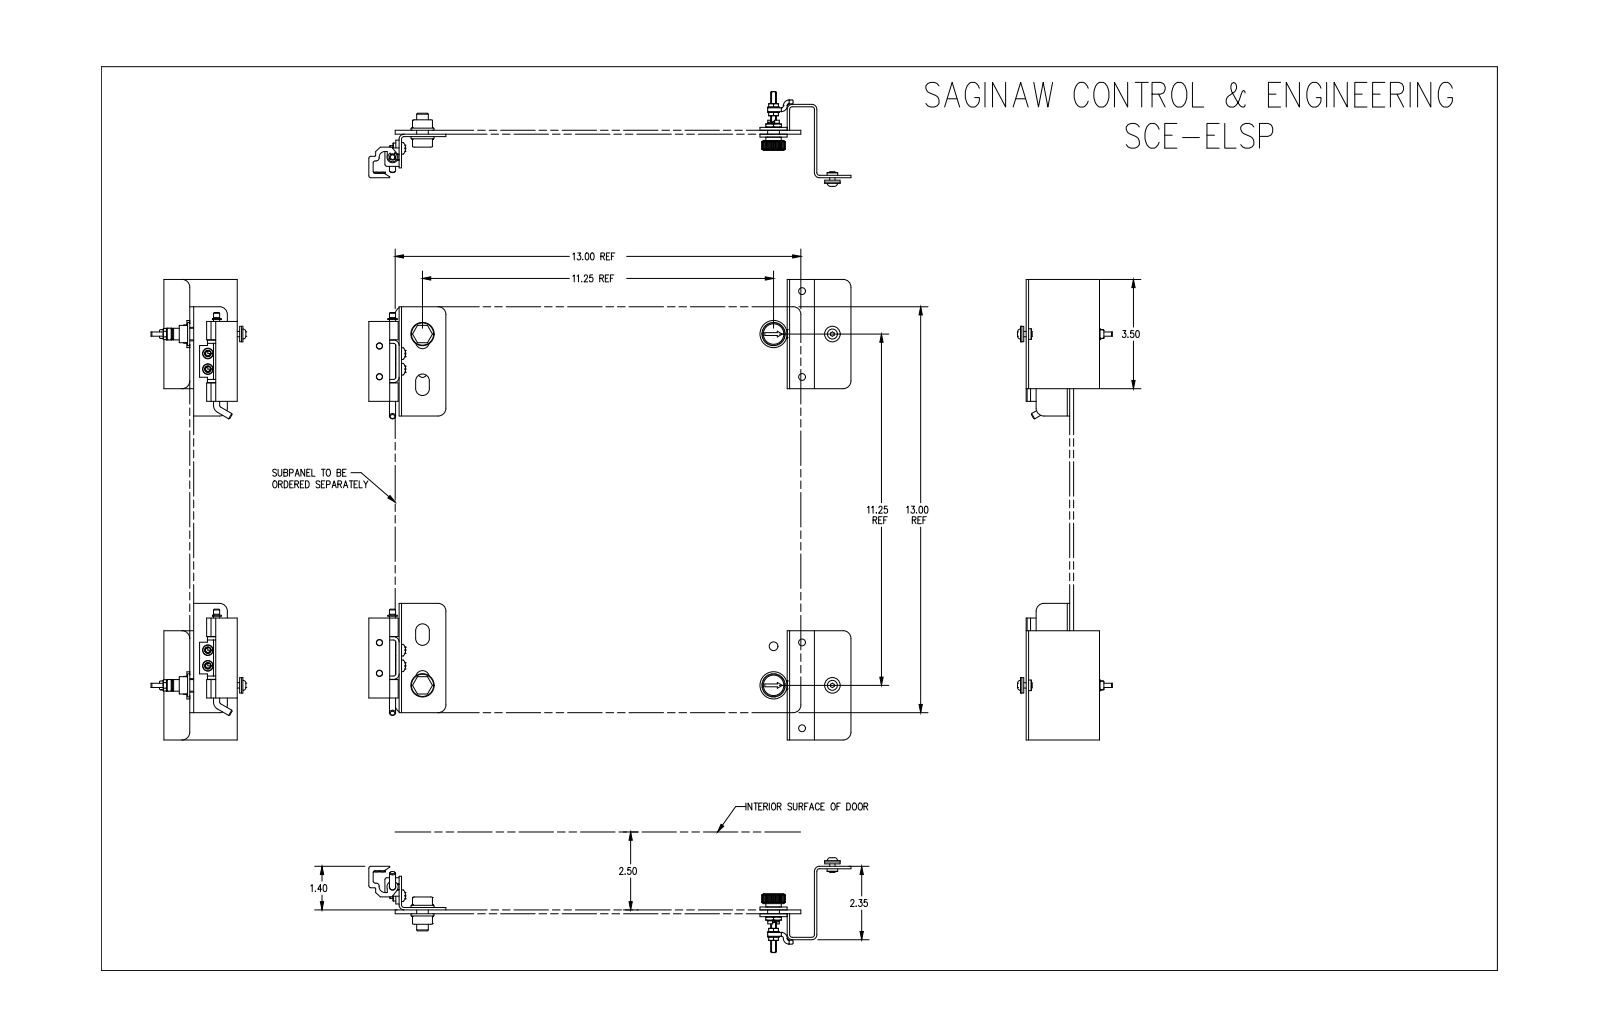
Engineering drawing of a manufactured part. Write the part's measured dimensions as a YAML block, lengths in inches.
part_name: "SCE-ELSP"
step_written_by: "SolidWorks 2021 (AUTOMOTIVE_DESIGN)"
units: inches
bodies: {solids: 61, faces: 1620, planar: 832, cylindrical: 392, other: 396}
overall_size: [15.457, 14.75, 3.083]
volume: 27.91
surface_area: 518.9
round_holes:
  - {diameter: 0.19, count: 8}
  - {diameter: 0.218, count: 8}
  - {diameter: 0.25, count: 6}
  - {diameter: 0.17, count: 4}
  - {diameter: 0.205, count: 4}
  - {diameter: 0.375, count: 4}
  - {diameter: 0.5, count: 4}
  - {diameter: 0.04, count: 2}
  - {diameter: 0.125, count: 2}
  - {diameter: 0.204, count: 2}
  - {diameter: 0.212, count: 2}
  - {diameter: 0.249, count: 2}
round_bosses_or_shafts:
  - {diameter: 0.373, count: 6}
  - {diameter: 0.34, count: 6}
  - {diameter: 0.249, count: 4}
  - {diameter: 0.24, count: 4}
  - {diameter: 0.188, count: 4}
  - {diameter: 0.196, count: 3}
  - {diameter: 0.136, count: 3}
  - {diameter: 0.87, count: 2}
partial_cylinders:
  - {radius: 0.031, count: 28}
  - {radius: 0.25, count: 20}
  - {radius: 0.01, count: 17}
  - {radius: 0.219, count: 8}
  - {radius: 0.07, count: 6}
  - {radius: 0.08, count: 5}
  - {radius: 0.104, count: 5}
  - {radius: 0.188, count: 5}
face_to_face_distances: [0.125, 0.078, 13.309, 1.317, 0.203, 0.125, 12.437, 0.872, 0.078, 0.955]
hole_center_spacings: [11.25, 11.25, 1.65, 1.65, 9.5, 0.494, 1.885, 9.917]
